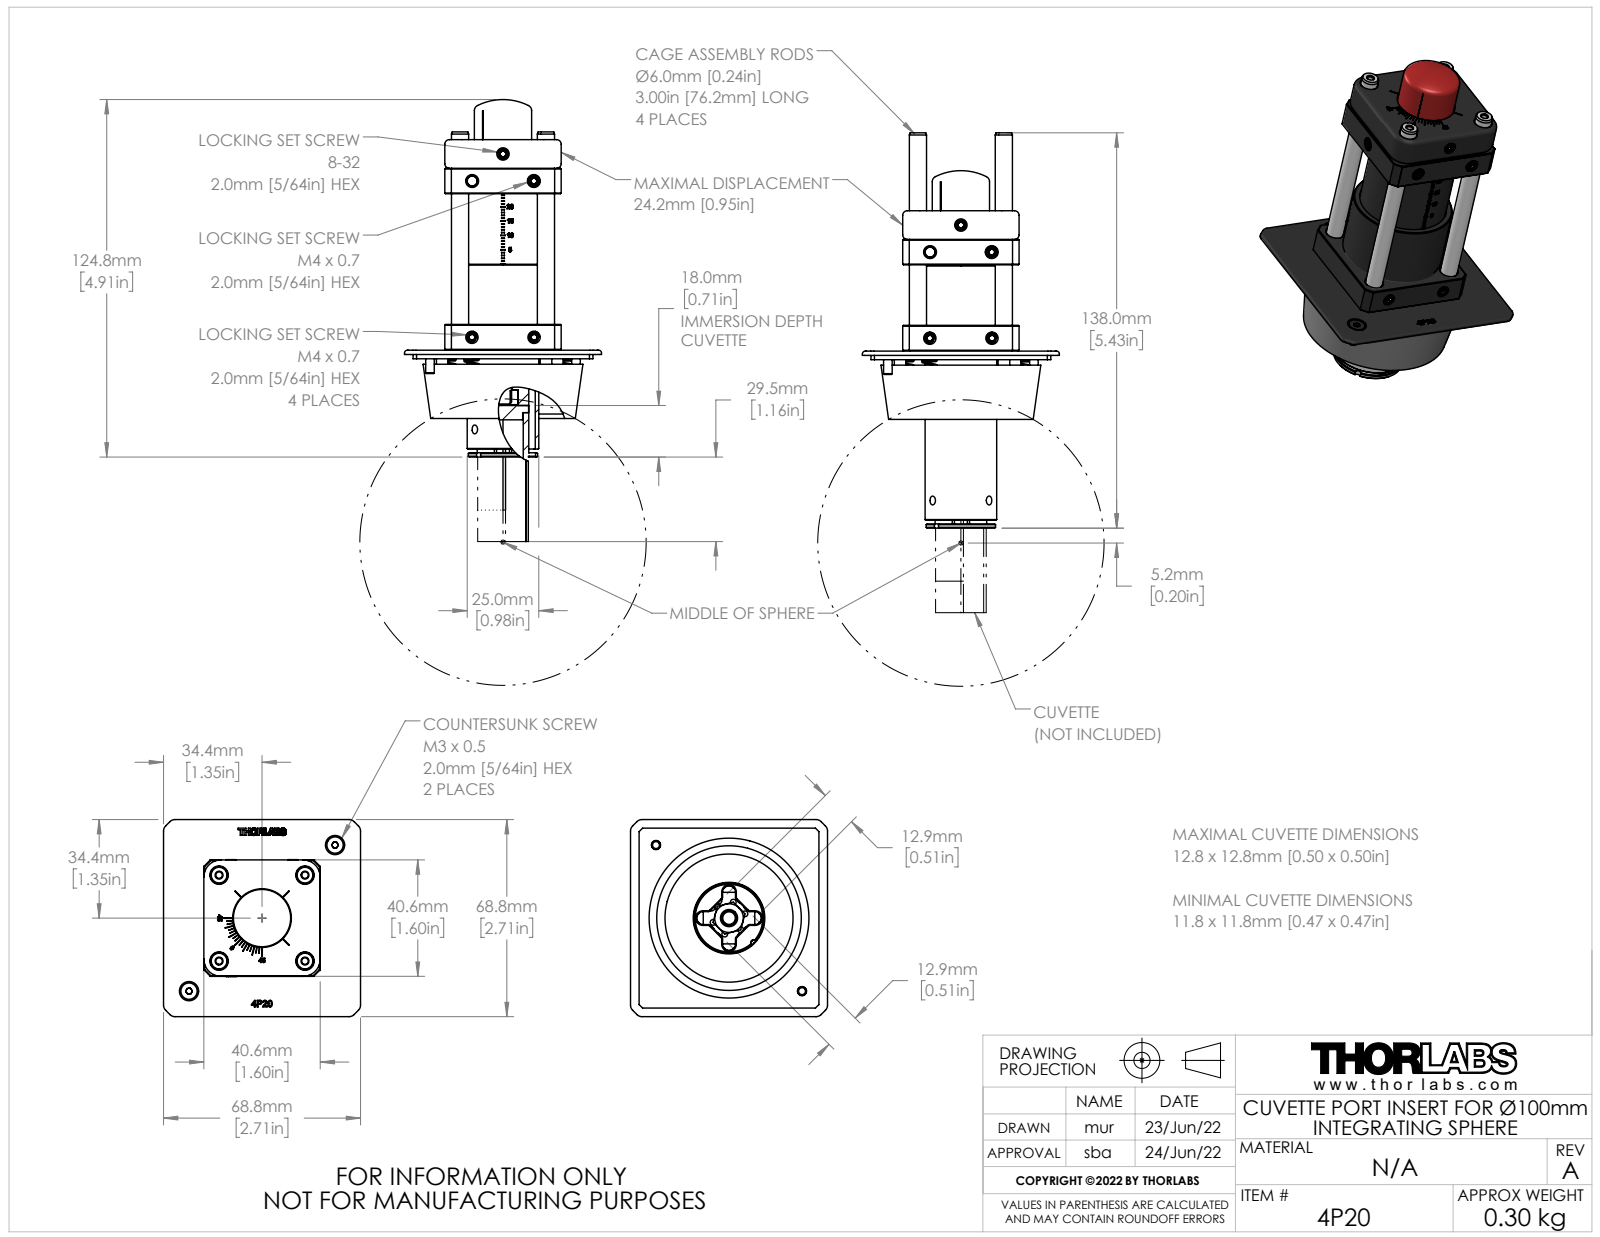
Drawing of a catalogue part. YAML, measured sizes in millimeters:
part_name: "22.07.20_4P20_Cuvette Port Insert f. D100mm IS WEB"
step_written_by: "SolidWorks 2019 (AUTOMOTIVE_DESIGN)"
units: millimeters
bodies: {solids: 51, faces: 2422, planar: 1459, cylindrical: 312, other: 651}
overall_size: [124.81, 68.8, 68.8]
volume: 111928
surface_area: 79610
round_holes:
  - {diameter: 2, count: 7}
  - {diameter: 3.1, count: 6}
  - {diameter: 3.3, count: 5}
  - {diameter: 4, count: 5}
  - {diameter: 2.26, count: 4}
  - {diameter: 2.7, count: 4}
  - {diameter: 6.02, count: 4}
  - {diameter: 6.5, count: 4}
  - {diameter: 4.5, count: 3}
  - {diameter: 5.5, count: 3}
  - {diameter: 2.9, count: 2}
  - {diameter: 3.2, count: 2}
round_bosses_or_shafts:
  - {diameter: 3.65, count: 5}
  - {diameter: 5.99, count: 4}
  - {diameter: 2.84, count: 4}
  - {diameter: 5.5, count: 3}
  - {diameter: 5.7, count: 2}
  - {diameter: 4, count: 2}
  - {diameter: 3, count: 2}
  - {diameter: 2.38, count: 2}
partial_cylinders:
  - {radius: 1, count: 19}
  - {radius: 1.75, count: 16}
  - {radius: 1.6, count: 12}
  - {radius: 2, count: 8}
  - {radius: 2.5, count: 8}
  - {radius: 1.8, count: 4}
  - {radius: 2.25, count: 4}
  - {radius: 6, count: 4}
face_to_face_distances: [3, 1.5, 4.9, 1.9, 63.5, 40.64, 66.5, 68.4, 9, 10]
hole_center_spacings: [5.77, 5.78, 10, 22, 5.69, 16.47, 16.49, 18.99]
